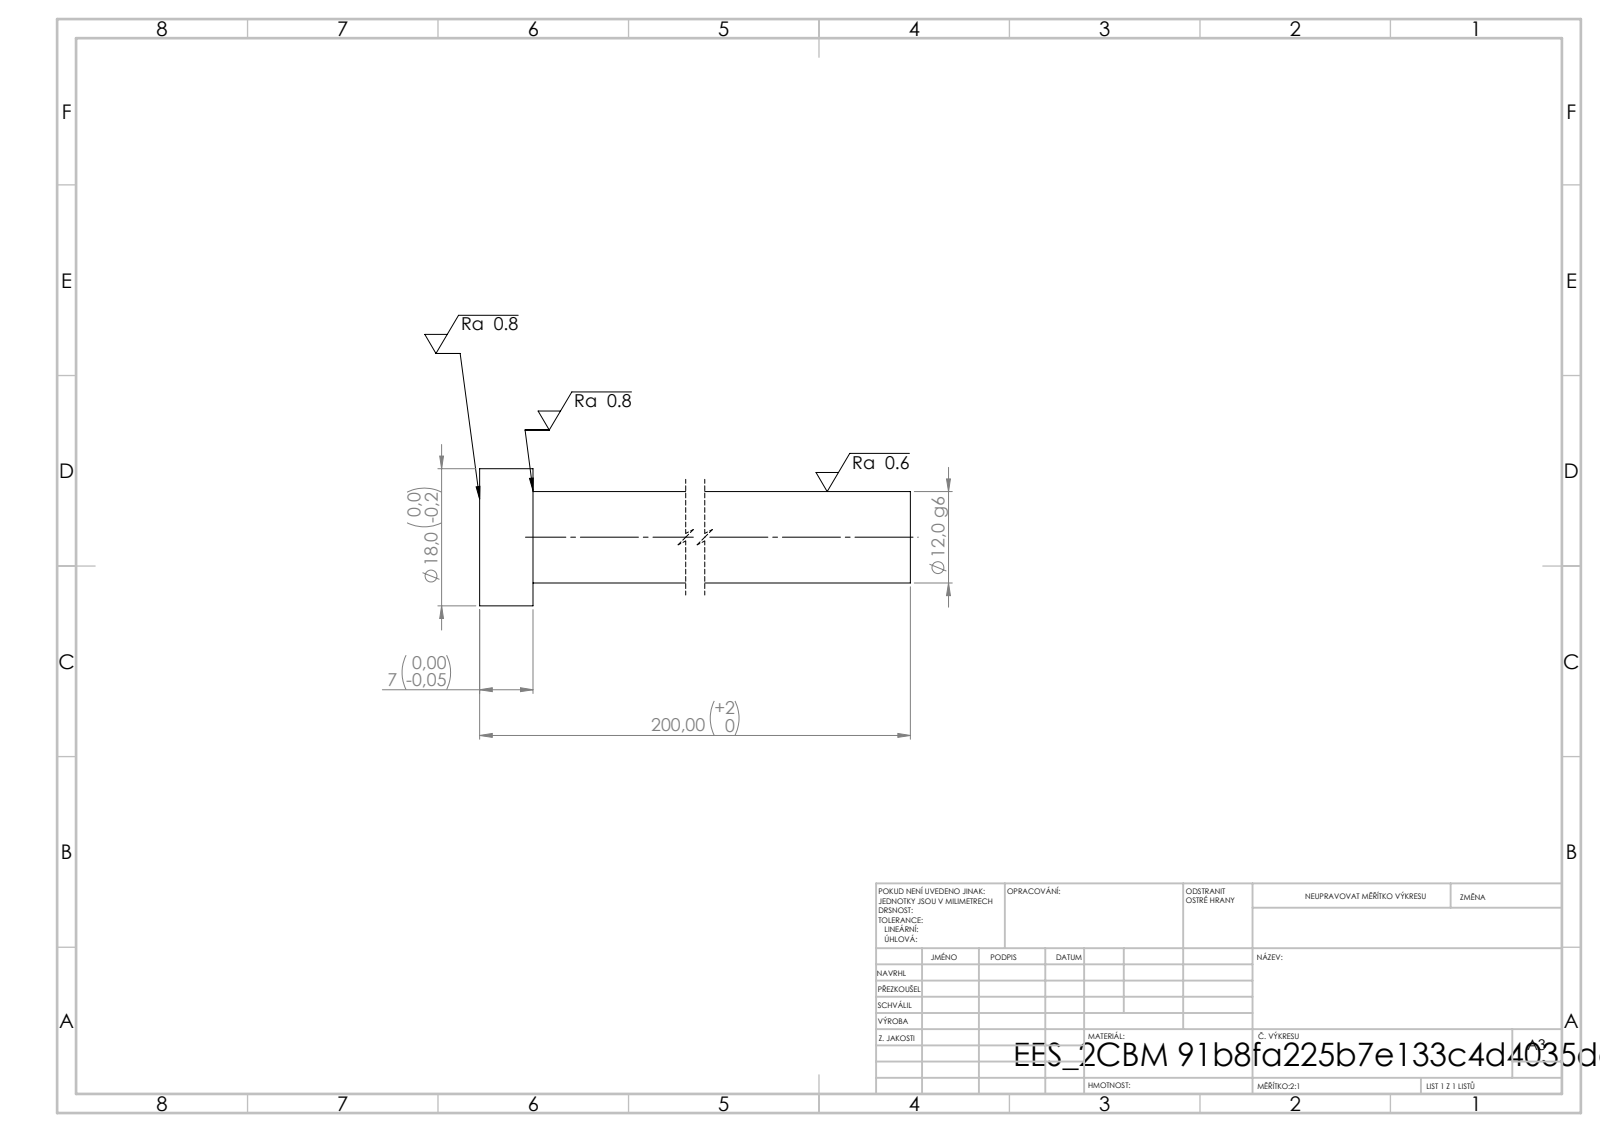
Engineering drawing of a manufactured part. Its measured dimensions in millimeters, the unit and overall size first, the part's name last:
Units: millimetres
Overall size (bounding box): 200 × 18 × 18
Round bosses / shafts (diameter × count): ⌀18 ×1, ⌀12 ×1
Main face-to-face distances: 7, 200, 193
Volume: 23 609 mm³ · Surface area: 8 181 mm²
Bodies: 1 solid, 7 faces (3 planar, 4 cylindrical, 0 other)
STEP written by: SolidWorks 2019 (CONFIG_CONTROL_DESIGN)
